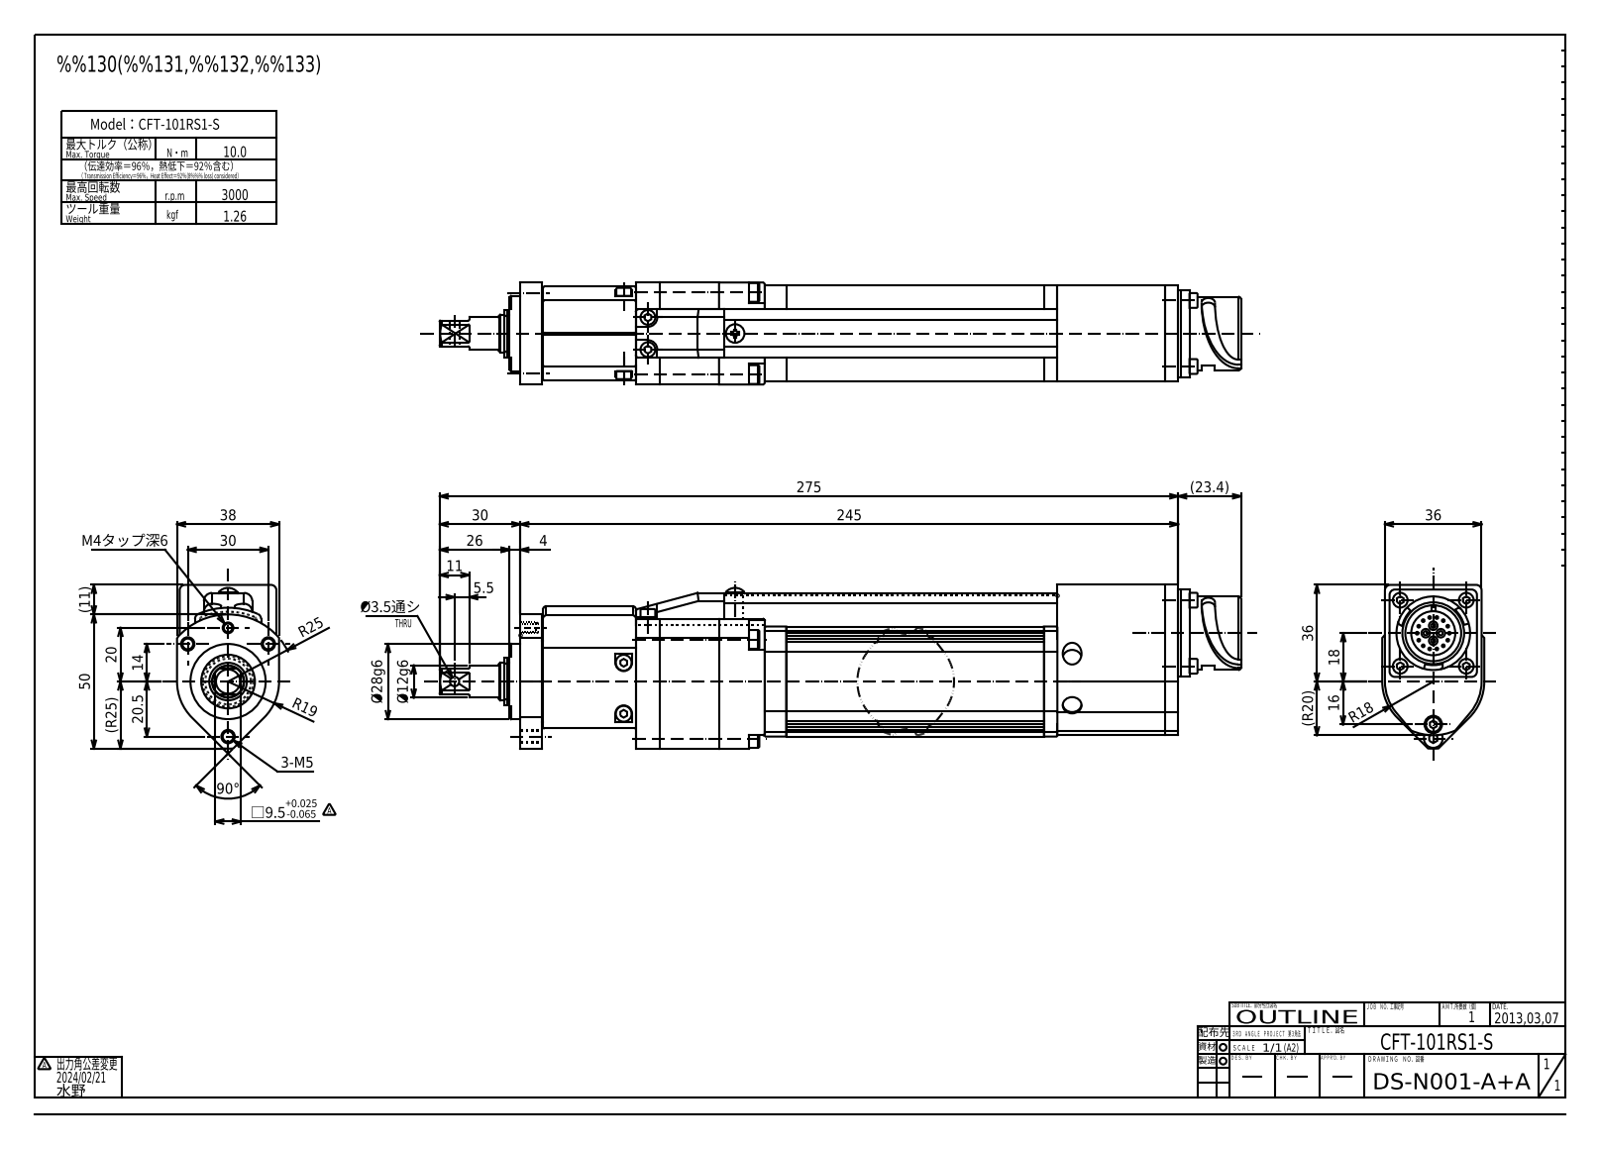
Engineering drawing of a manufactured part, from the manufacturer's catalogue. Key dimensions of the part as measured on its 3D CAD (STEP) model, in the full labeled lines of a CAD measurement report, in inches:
Part name (STEP PRODUCT): CFT-101RS1-S
STEP written by: SolidWorks 2013 (CONFIG_CONTROL_DESIGN)
Units: inches
Bodies: 17 solids, 326 faces (140 planar, 136 cylindrical, 50 other)
Overall size (bounding box): 11.709 × 2.402 × 1.5
Volume: 21.46 in³ · Surface area: 128.1 in²
Round holes (diameter × count): ⌀0.165 ×3, ⌀0.13 ×1, ⌀0.138 ×1, ⌀0.819 ×1
Round bosses / shafts (diameter × count): ⌀0.217 ×6, ⌀0.295 ×3, ⌀1.26 ×1, ⌀1.102 ×1, ⌀1.079 ×1, ⌀0.551 ×1, ⌀0.472 ×1, ⌀0.26 ×1
Partial cylindrical surfaces — rounded edges, fillets, slot ends (radius × count): R0.079 ×12, R0.02 ×7, R0.039 ×4, R0.118 ×4, R0.177 ×3, R0.138 ×2, R0.197 ×2, R0.709 ×1
Main face-to-face distances: 0.354, 0.039, 1.811, 5.787, 1.063, 0.669, 0.315, 3.543, 0.394, 0.433
Hole centre spacings: 0.622, 0.636, 1.481, 0.039, 1.181, 1.555, 1.594
